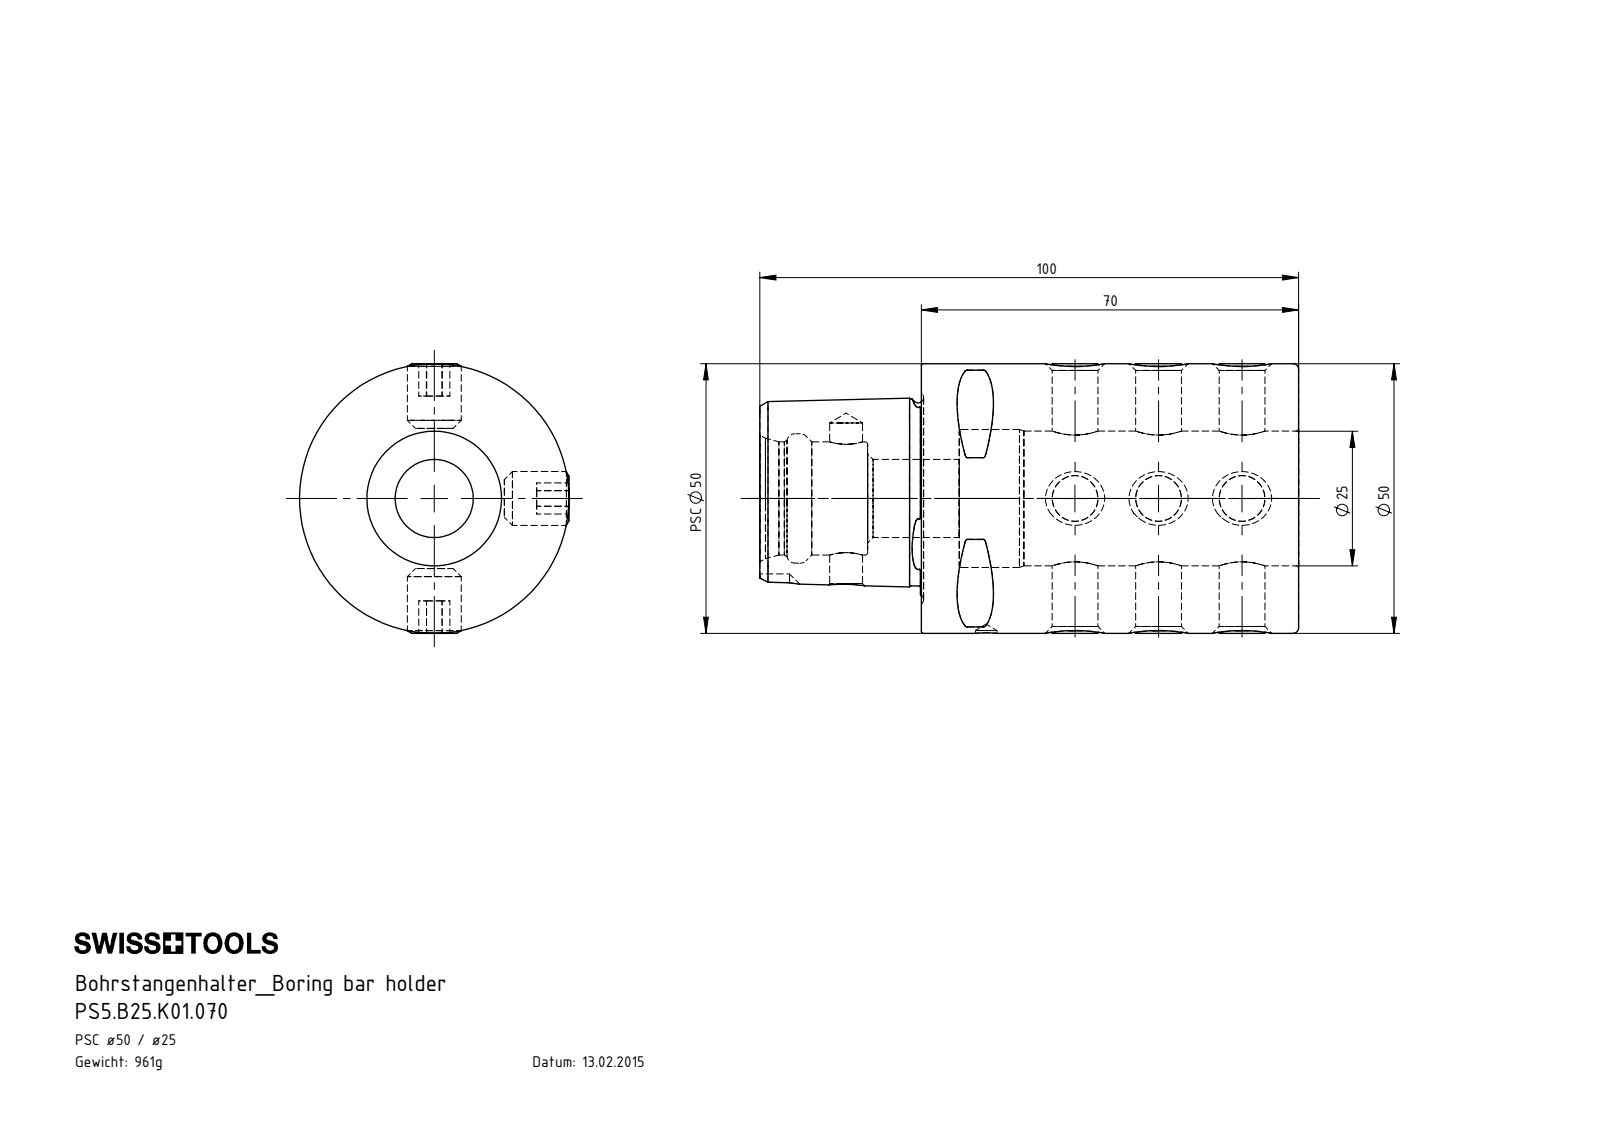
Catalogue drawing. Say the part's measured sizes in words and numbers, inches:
The part is named "PS5-B25.K01.070_A; ISO 4026 - M10 x 12_PreviewCfg; PS5.B25.K01.070". Its 3-D file was written by "SolidWorks 2017 (AUTOMOTIVE_DESIGN)". It is 10 solids with 315 faces: 101 planar, 65 cylindrical and 149 other. Overall it measures 3.937 by 1.969 by 1.969 inches. Its volume is 7.464 cubic inches and its surface area 49.94 square inches. Round holes: 6 of diameter 0.335, 1 of diameter 0.157, 1 of diameter 0.24, 1 of diameter 0.571, 1 of diameter 0.827, 1 of diameter 0.945, 1 of diameter 0.984, 1 of diameter 1.008. Round bosses or shafts: 6 of diameter 0.394, 1 of diameter 1.969. Partial cylindrical surfaces (rounded edges, fillets, slot ends): 8 of radius 0.02, 1 of radius 0.157. The main face-to-face distances are 2.756, 0.197, 1.181, 3.937, 0.236, 1.457, 0.276, 2.48, 0.305, 0.755. The hole center spacings are 0.61, 1.22, 0.65, 1.024, 1.26, 1.673, 1.87, 2.283.
